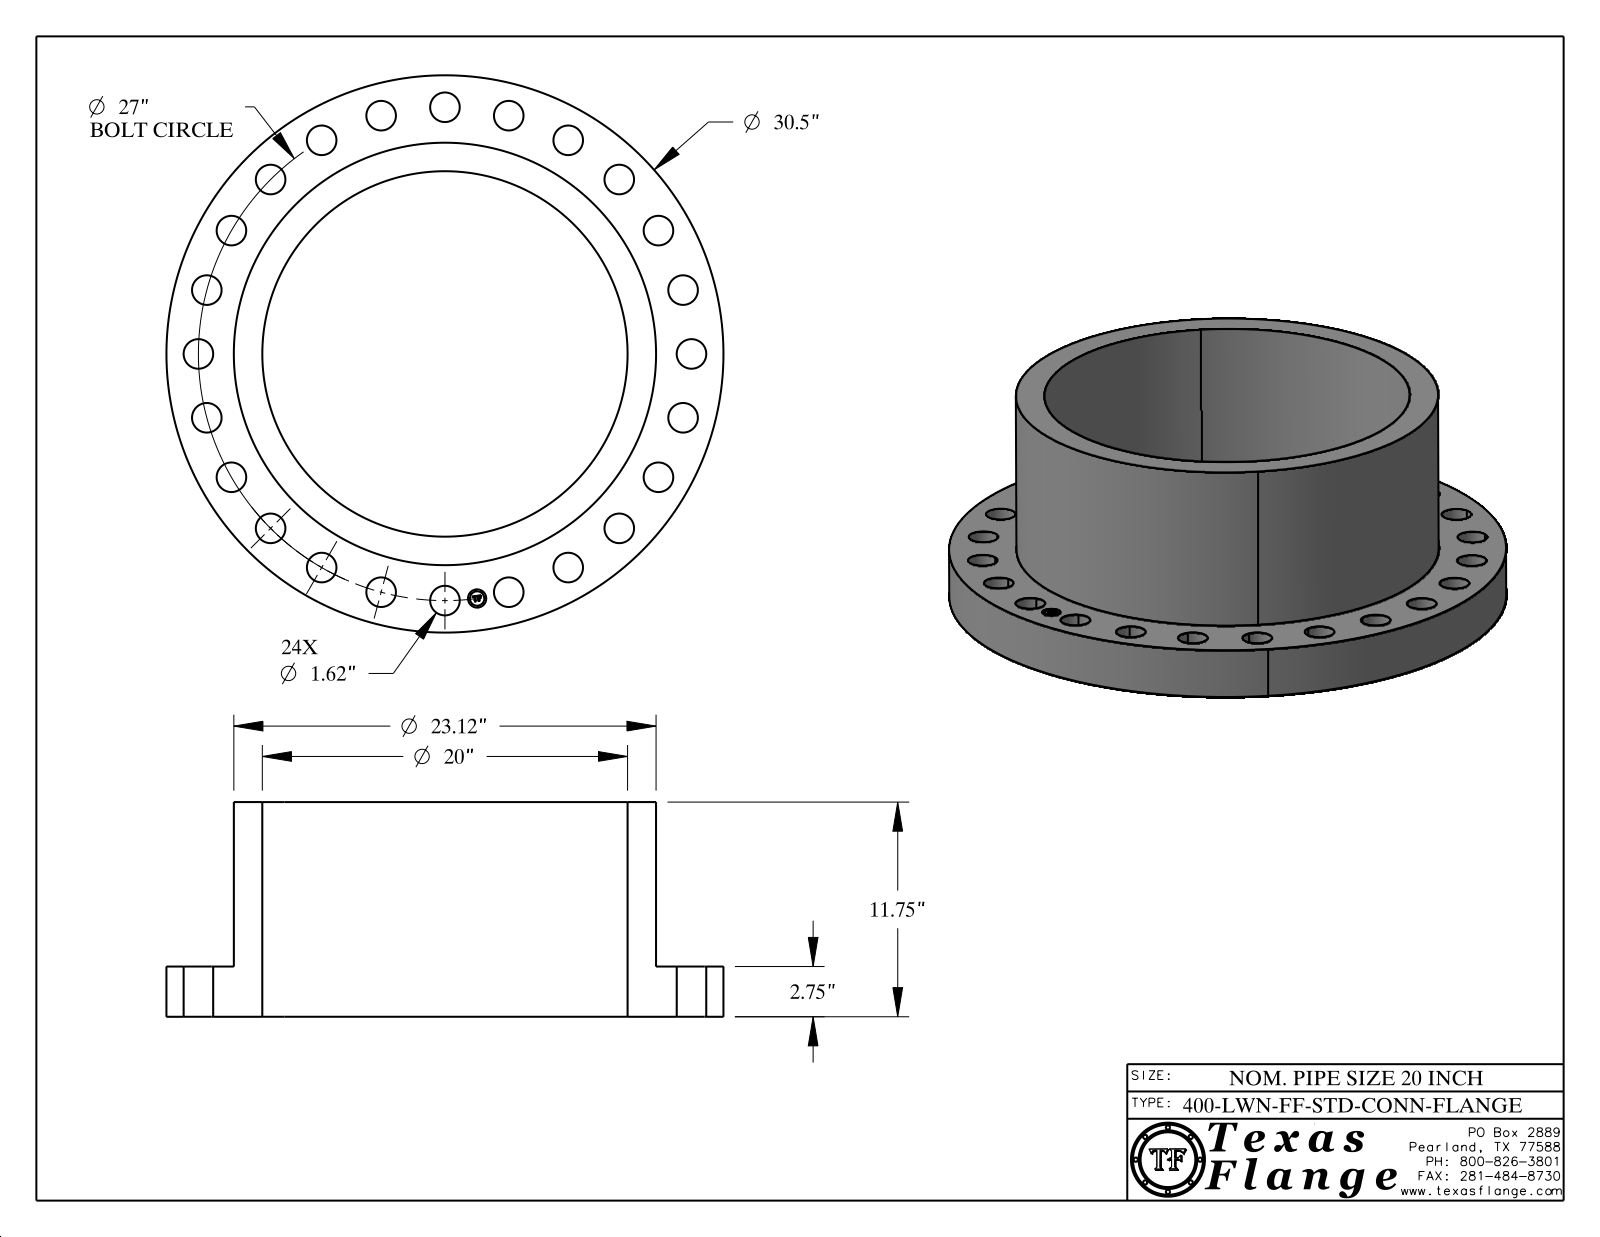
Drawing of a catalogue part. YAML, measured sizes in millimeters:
part_name: "20-400-LWN-FF-STD-CONN-FLANGE"
step_written_by: "CATIA V5 STEP AP214 (AUTOMOTIVE_DESIGN)"
units: millimeters
bodies: {solids: 1, faces: 442, planar: 368, cylindrical: 74, other: 0}
overall_size: [774.7, 774.7, 298.5]
volume: 32120000
surface_area: 1758000
round_holes:
  - {diameter: 41.1, count: 24}
  - {diameter: 25.4, count: 1}
  - {diameter: 508, count: 1}
round_bosses_or_shafts:
  - {diameter: 1.5, count: 8}
  - {diameter: 774.7, count: 1}
  - {diameter: 587.2, count: 1}
  - {diameter: 20, count: 1}
face_to_face_distances: [69.9, 298.5, 228.6, 69.7, 228.7, 7.6, 7.4, 1.4, 4.9, 6.3]
hole_center_spacings: [342.9, 89.5, 177.5, 262.5, 417.5, 633.6, 679.9, 544.1]
